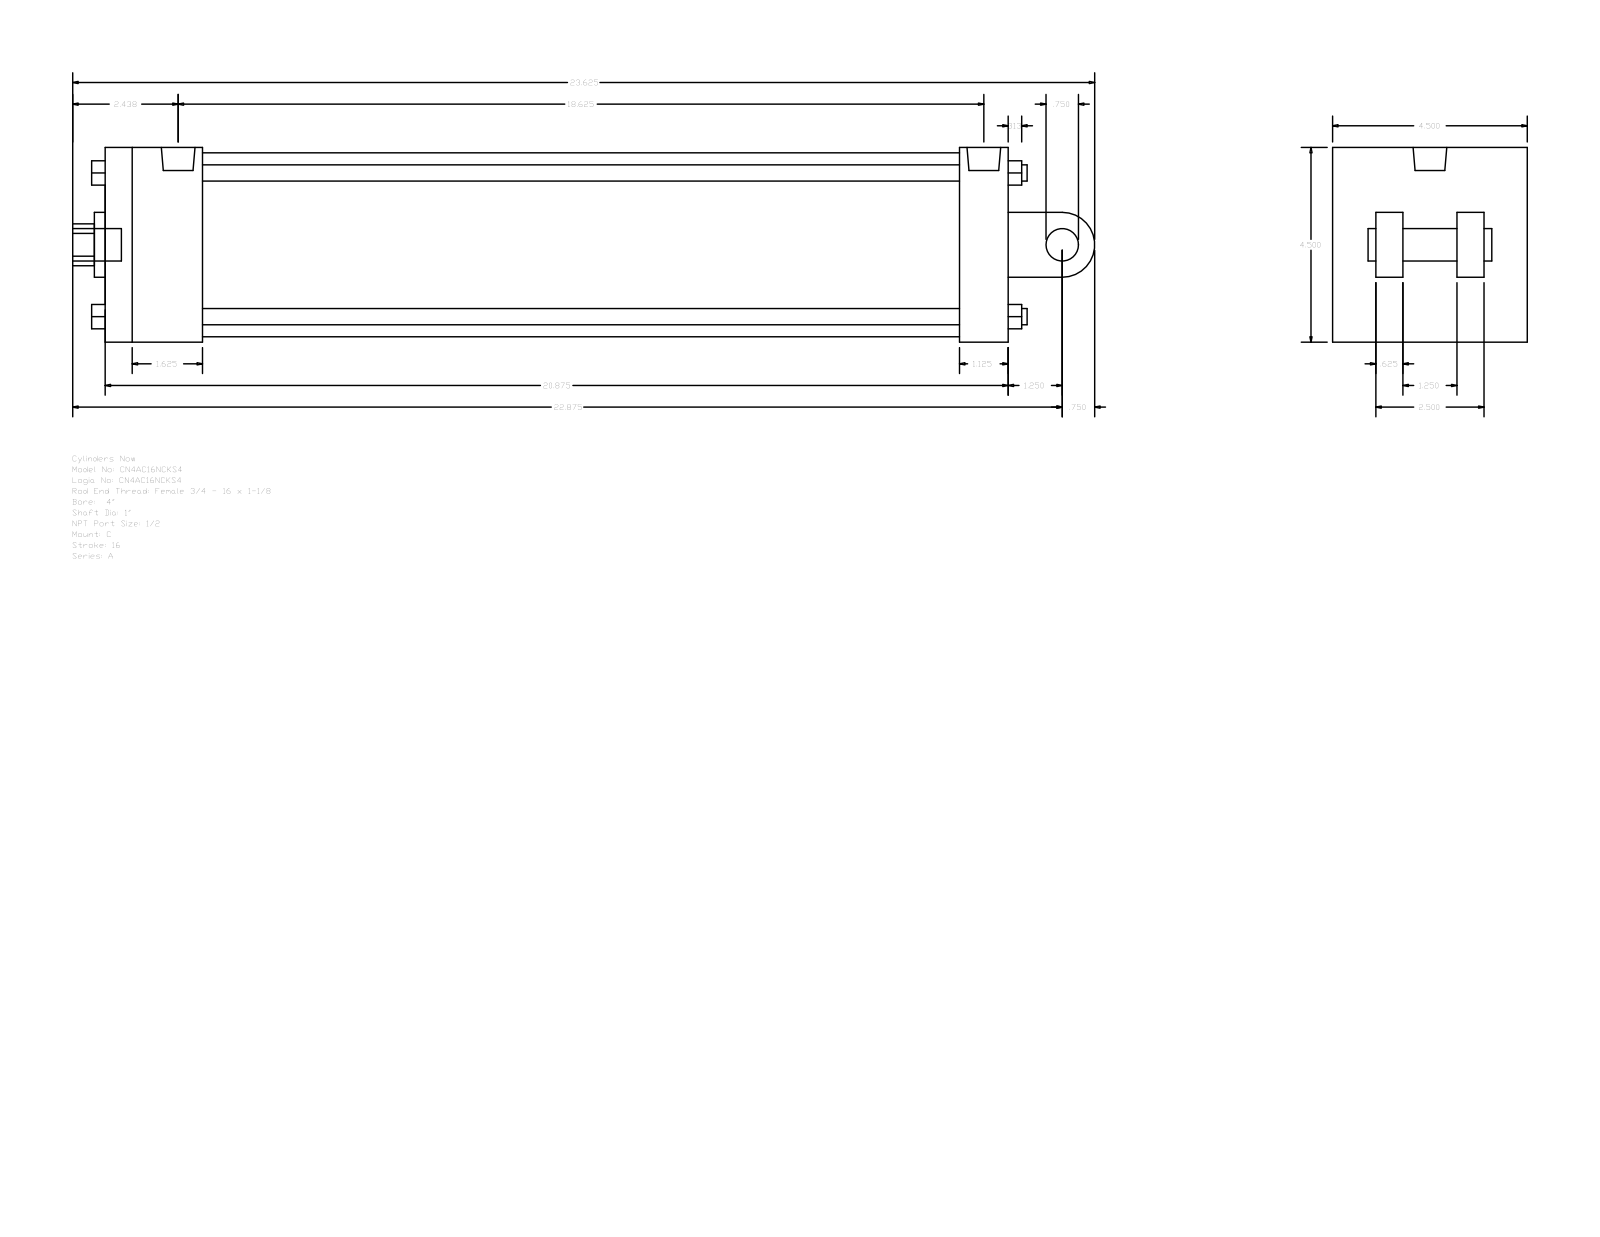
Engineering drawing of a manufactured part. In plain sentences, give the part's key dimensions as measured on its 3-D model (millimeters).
The part is named "A_C__0400_1". Its 3-D file was written by "GSSL Pune (CONFIG_CONTROL_DESIGN)". It is 0 solids with 135 faces: 102 planar, 33 cylindrical and 0 other. Overall it measures 600.08 by 114.3 by 114.3 millimeters. Round holes: 2 of diameter 8.73, 1 of diameter 19.77, 1 of diameter 25.4, 1 of diameter 38.1, 1 of diameter 107.95. Round bosses or shafts: 4 of diameter 9.53, 2 of diameter 19.05, 2 of diameter 8.73, 1 of diameter 19.77. Partial cylindrical surfaces (rounded edges, fillets, slot ends): 1 of radius 12.29, 1 of radius 19.05. The main face-to-face distances are 114.3, 530.22, 73.03, 28.57, 501.65, 57.15, 444.5, 473.07, 15.87, 47.63. The hole center spacings are 3.18.
